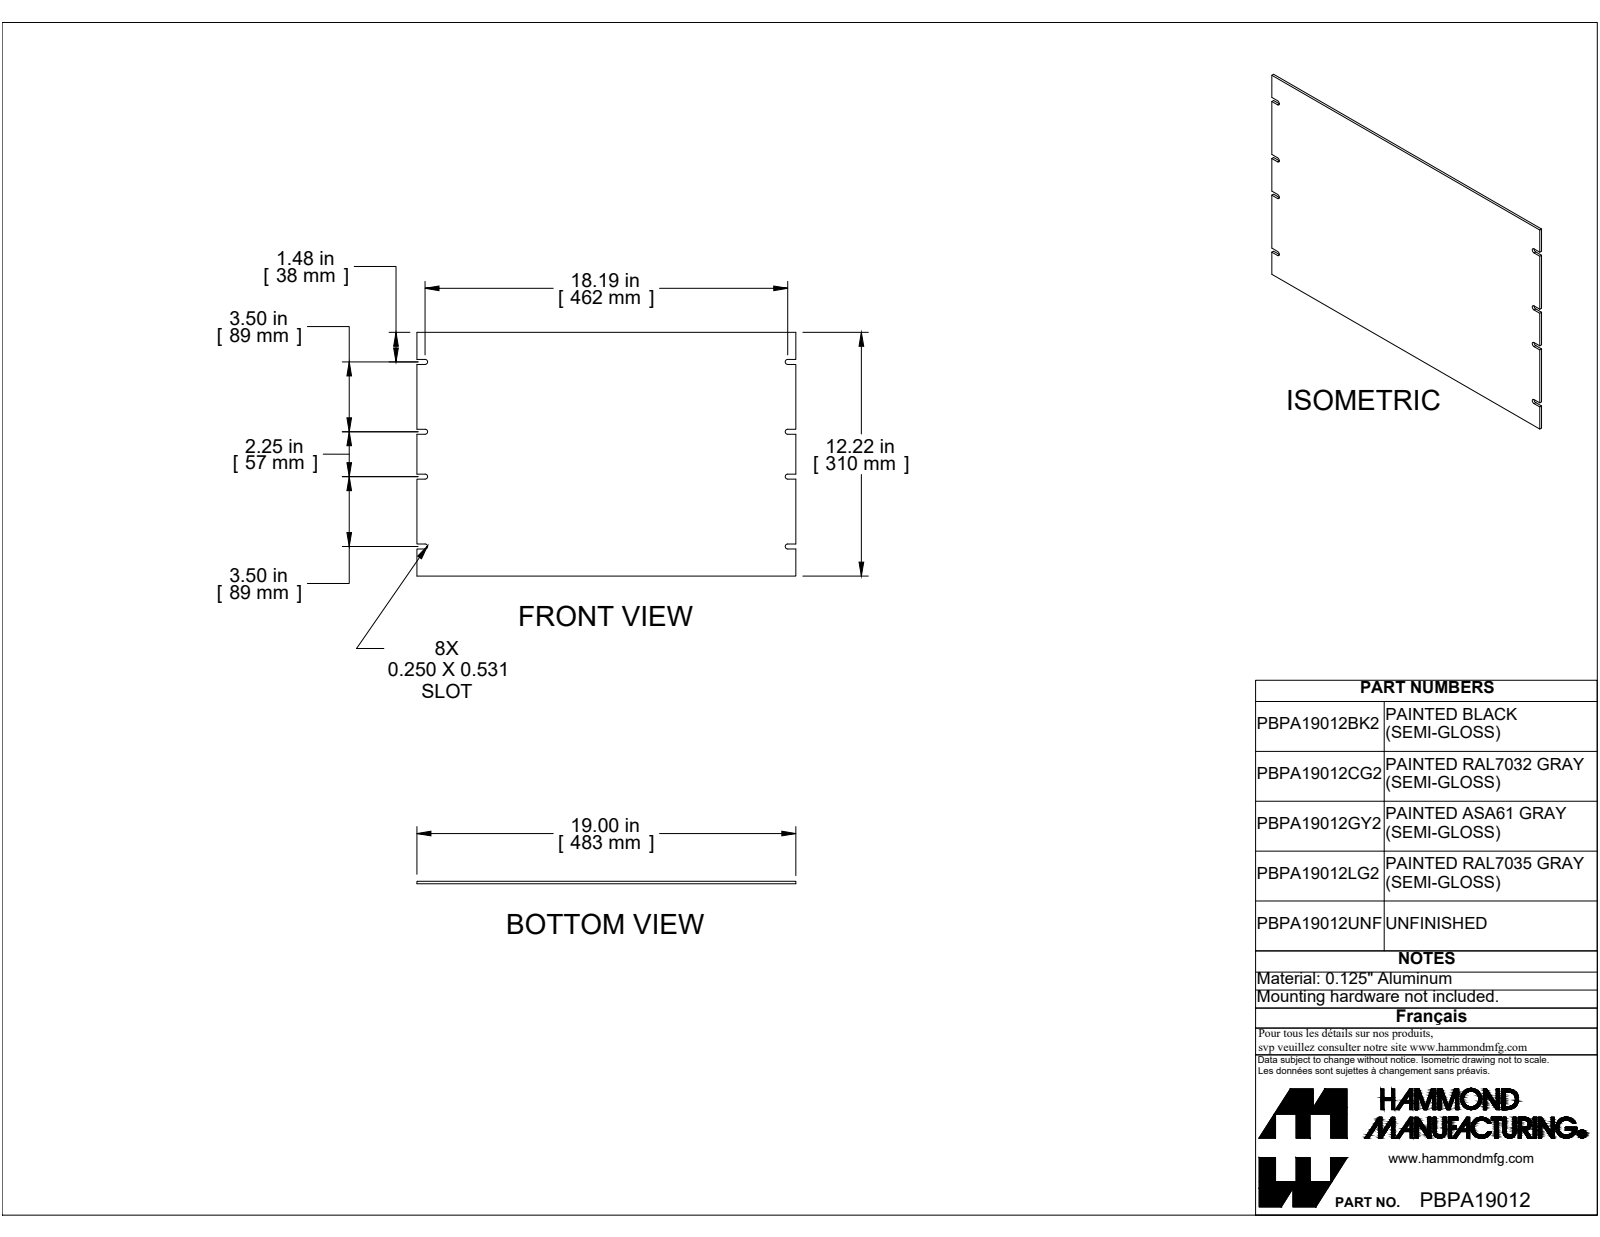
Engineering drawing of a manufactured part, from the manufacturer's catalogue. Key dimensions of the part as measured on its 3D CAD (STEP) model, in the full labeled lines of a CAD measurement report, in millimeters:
Part name (STEP PRODUCT): PBPA19012UNF
STEP written by: SolidWorks 2019 (CONFIG_CONTROL_DESIGN)
Units: millimetres
Bodies: 1 solid, 38 faces (30 planar, 8 cylindrical, 0 other)
Overall size (bounding box): 482.6 × 310.3 × 3.2
Volume: 473 400 mm³ · Surface area: 303 900 mm²
Partial cylindrical surfaces — rounded edges, fillets, slot ends (radius × count): R3.2 ×8
Main face-to-face distances: 3.2, 310.3, 482.6, 88.9, 146.1, 6.4, 34.5, 40.9, 123.4, 129.8
